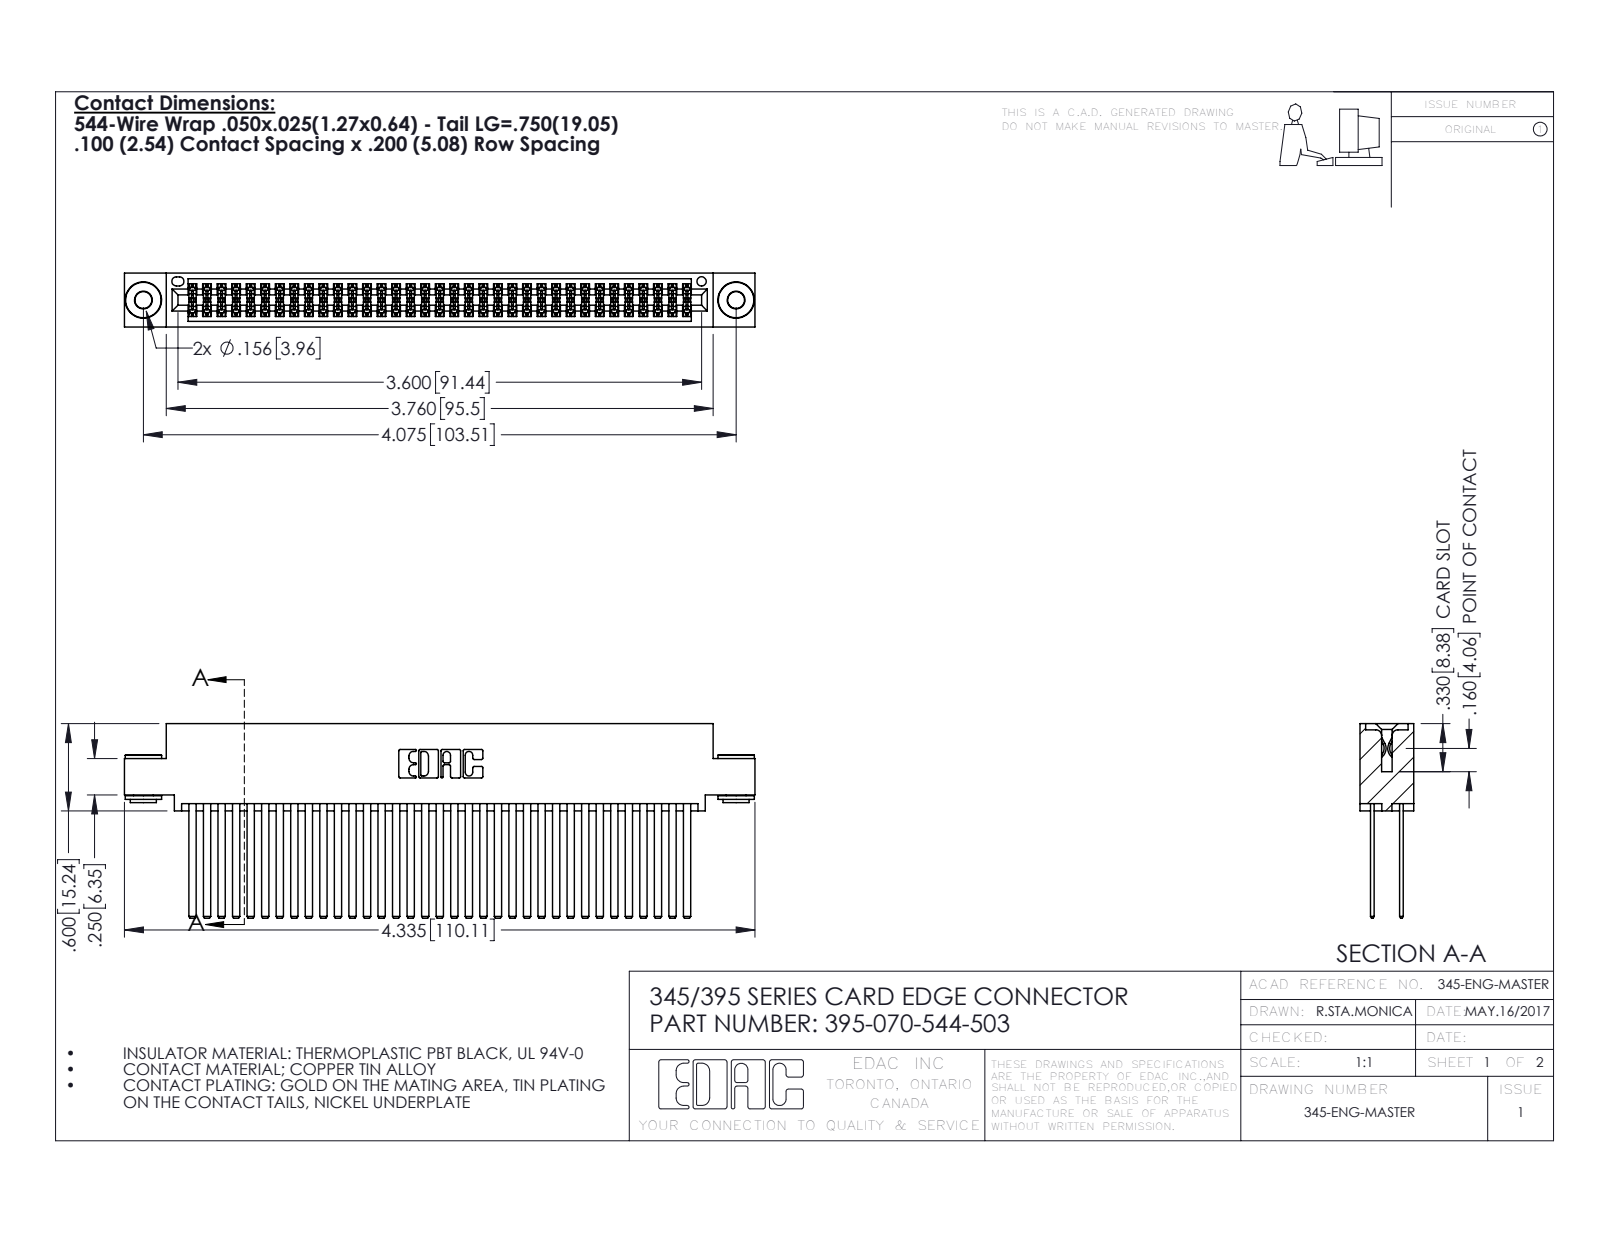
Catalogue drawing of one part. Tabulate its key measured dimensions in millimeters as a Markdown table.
| quantity | value |
| --- | --- |
| part name | 345-250-002_345-250-002-102; 345-292-001_345-293-144; 395-070-544-503; 345 Part_0.110 Offset - 0.156 Dia-TH |
| STEP written by | SolidWorks 2016 (CONFIG_CONTROL_DESIGN) |
| units | millimeters |
| bodies | 73 solids, 3248 faces (2124 planar, 1116 cylindrical, 8 other) |
| overall size | 110.1 × 34 × 9.4 |
| volume | 11 600 mm³ |
| surface area | 20 120 mm² |
| round holes (diameter × count) | 2.9 × 2, 4 × 2, 1.6 × 1 |
| round bosses / shafts (diameter × count) | 6.4 × 2, 4.6 × 2, 3.5 × 2 |
| partial cylindrical surfaces (radius × count) | 0.2 × 105, 0.3 × 22, 0.2 × 6, 0.8 × 6, 0.7 × 3, 0.4 × 2, 0.5 × 2, 0.6 × 2 |
| main face-to-face distances | 5.1, 0.6, 1.8, 2.5, 6.9, 7.6, 5.7, 4.4, 9.4, 1.3 |
| hole center spacings | 6.9, 97.5, 103.5 |
